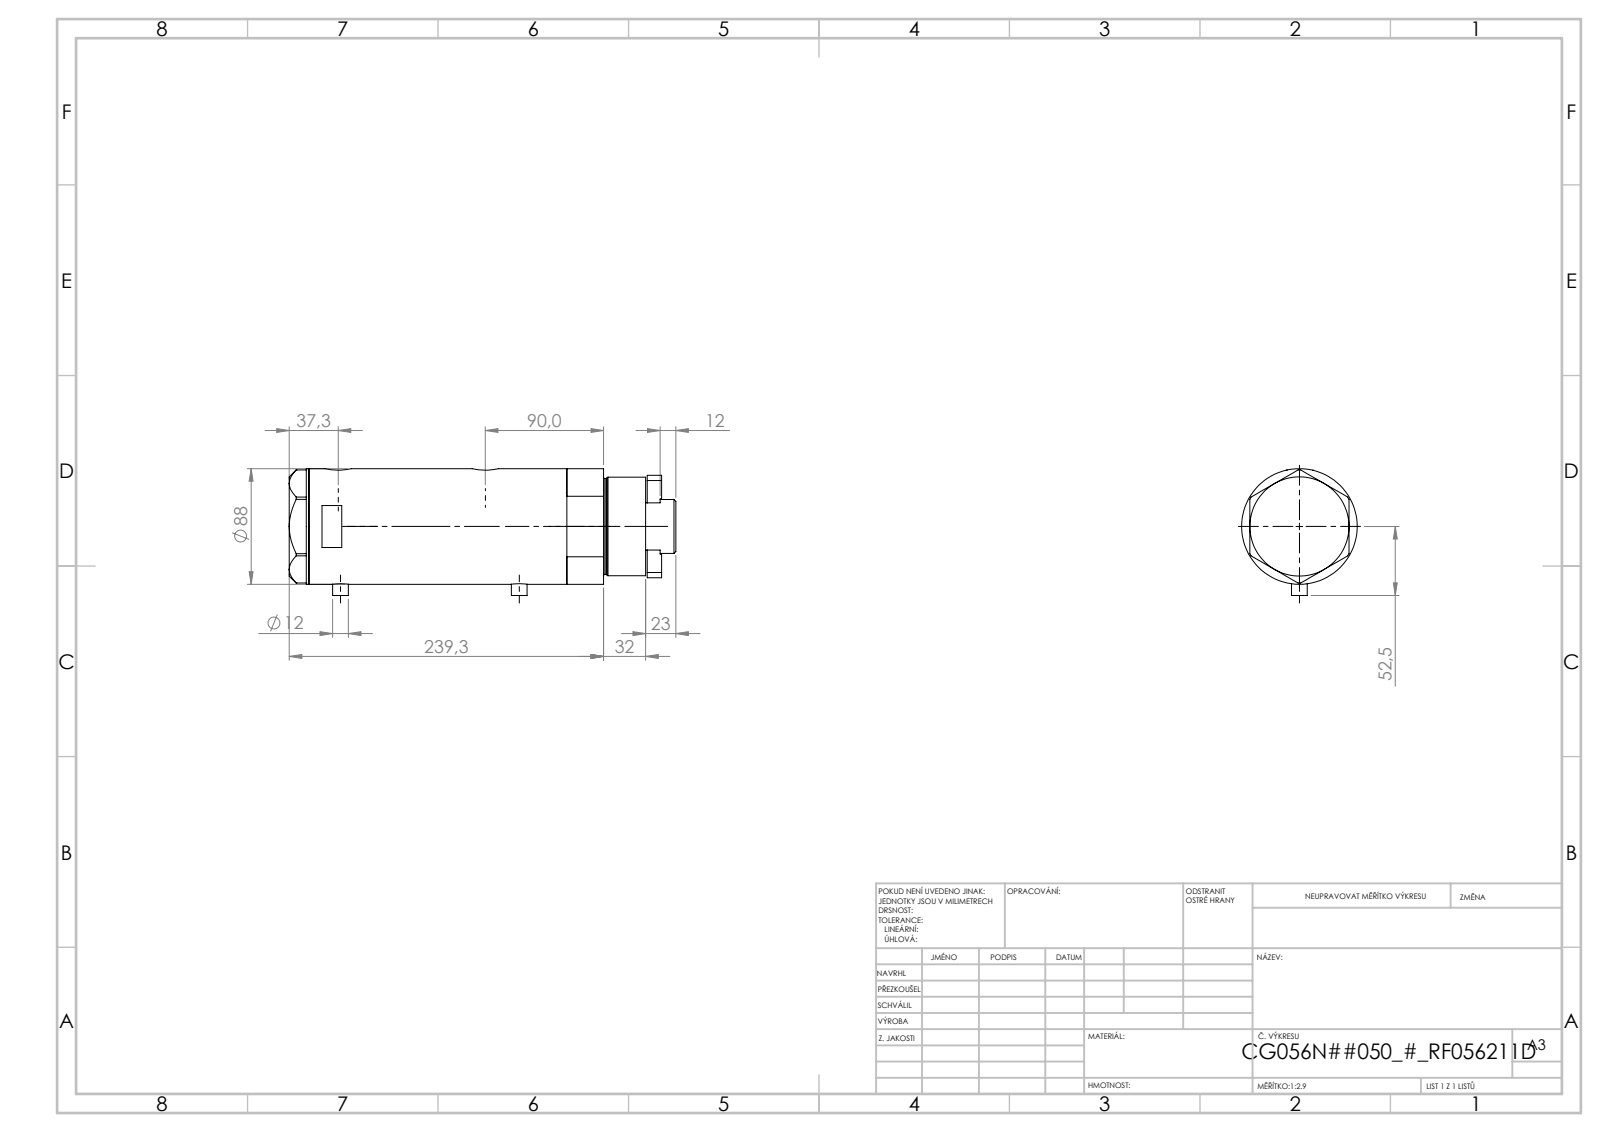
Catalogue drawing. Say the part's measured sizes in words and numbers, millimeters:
The part is named "V270CG_BACK; V270CG_MIDDLE; V270CG_FRONT; V270CG_VC (+1 more)". Its 3-D file was written by "SolidWorks 2019 (CONFIG_CONTROL_DESIGN)". It is 6 solids with 166 faces: 77 planar, 69 cylindrical and 20 other. Overall it measures 274.47 by 89.1 by 88 millimeters. Its volume is 1 423 000 cubic millimeters and its surface area 216 111 square millimeters. Round holes: 4 of diameter 8.1, 4 of diameter 13.5, 2 of diameter 5, 2 of diameter 12.5, 2 of diameter 13.16, 2 of diameter 20, 1 of diameter 14.5, 1 of diameter 42, 1 of diameter 43.5, 1 of diameter 56, 1 of diameter 60, 1 of diameter 80. Round bosses or shafts: 2 of diameter 12, 1 of diameter 88, 1 of diameter 75, 1 of diameter 73, 1 of diameter 41. The main face-to-face distances are 124.4, 26, 98.4, 15, 41, 139.4, 236.47, 251.47, 210.47, 112.07. The hole center spacings are 30.35, 18, 57.96, 60.69, 1.7, 25.8, 100.3, 102.
